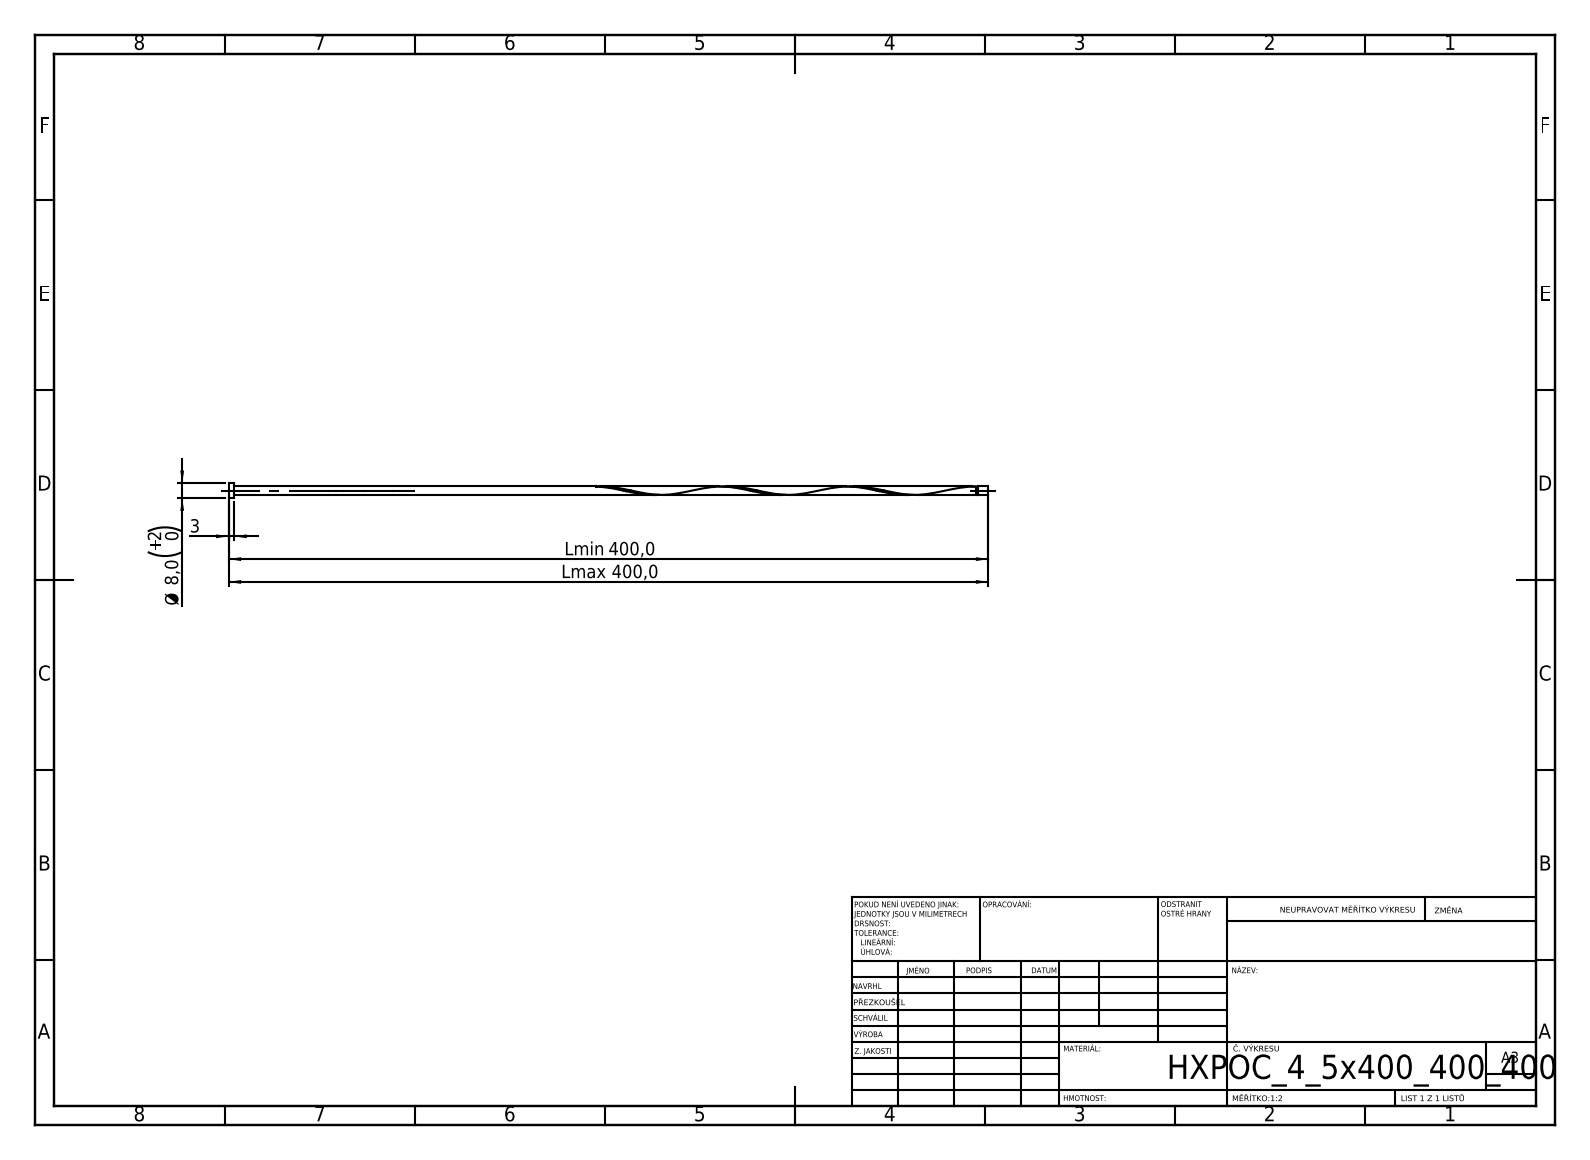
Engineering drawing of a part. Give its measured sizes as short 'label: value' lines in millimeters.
written by: SolidWorks 2019 (CONFIG_CONTROL_DESIGN)
unit: mm
bodies: 1 solid, 16 faces (6 planar, 9 cylindrical, 1 other)
size: 400 × 8 × 8
volume: 7 813 mm³; area: 7 770 mm²
bosses: 1× ⌀8, 1× ⌀4.5, 1× ⌀3.6
face distances: 3, 400, 397, 394.51, 391.51, 5.49, 393.61, 390.61, 0.9, 6.39
